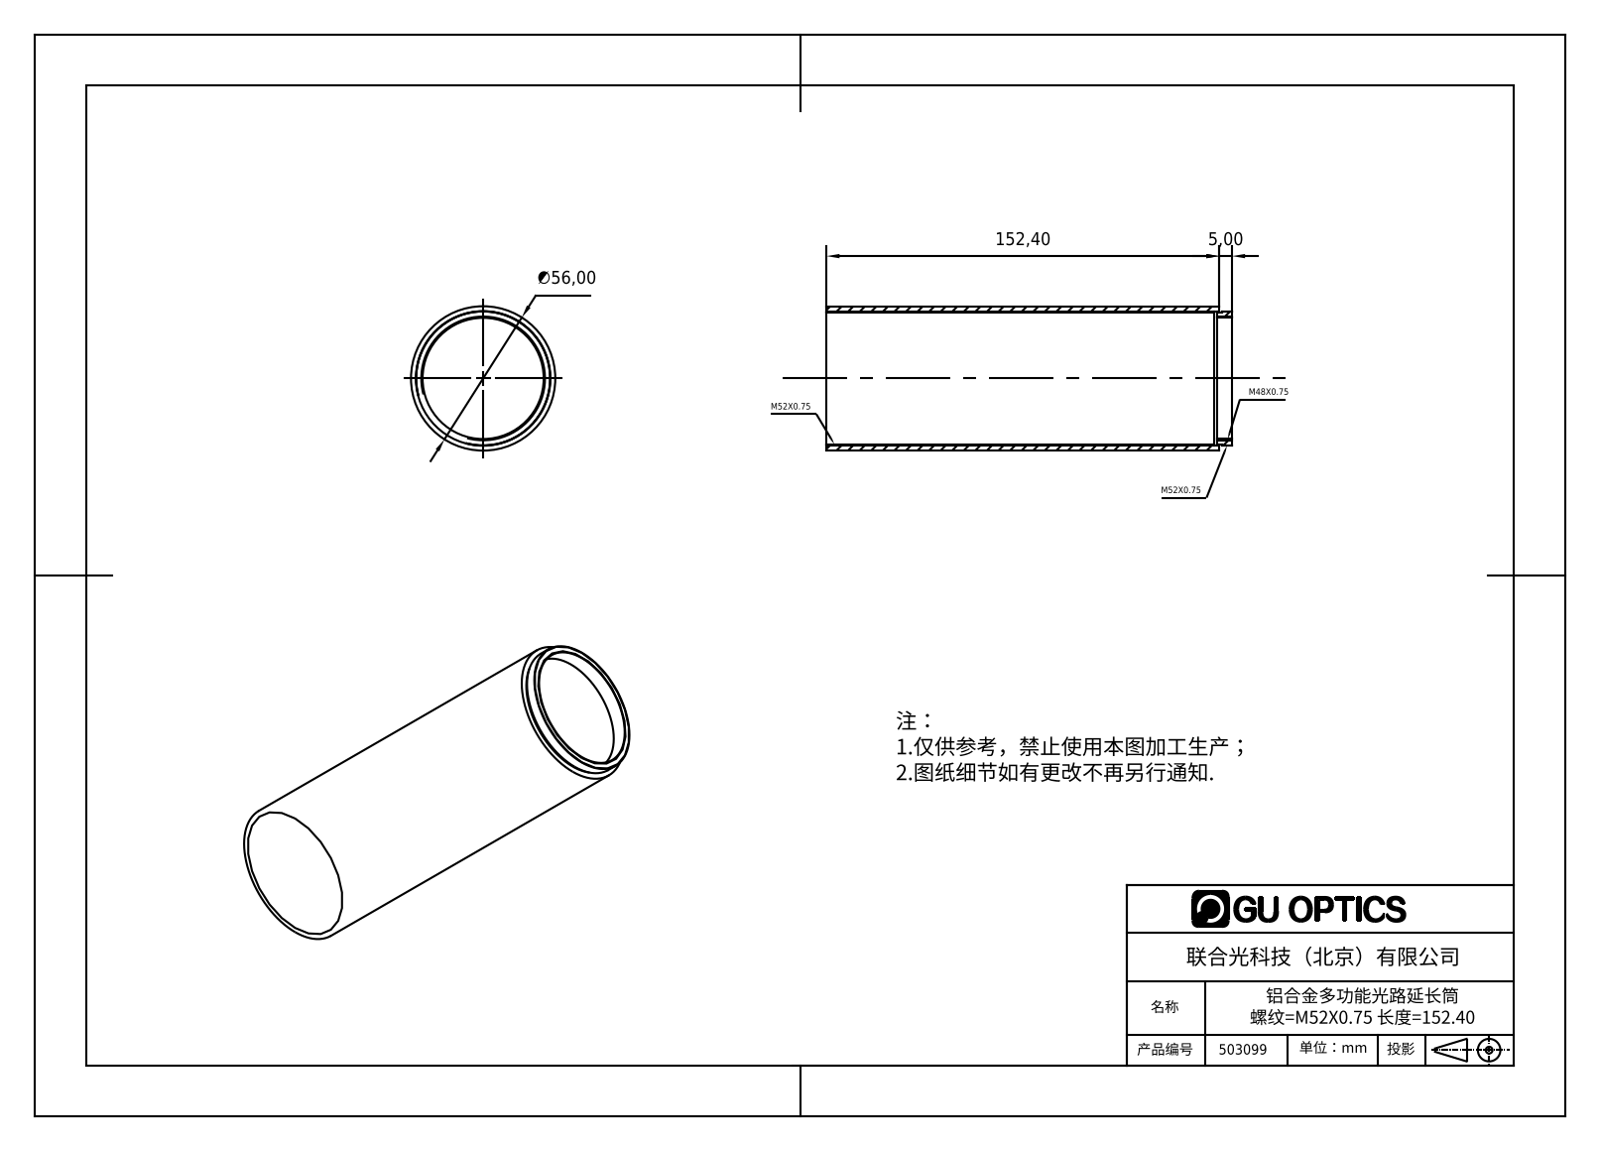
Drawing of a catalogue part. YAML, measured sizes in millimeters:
part_name: "503099"
step_written_by: "SolidWorks 2016 (AUTOMOTIVE_DESIGN)"
units: millimeters
bodies: {solids: 1, faces: 18, planar: 6, cylindrical: 12, other: 0}
overall_size: [157.4, 56, 56]
volume: 66176
surface_area: 54620
round_holes:
  - {diameter: 47, count: 1}
  - {diameter: 51, count: 1}
  - {diameter: 52.2, count: 1}
round_bosses_or_shafts:
  - {diameter: 56, count: 1}
face_to_face_distances: [1, 152.4, 157.4, 5, 151.4, 6, 2, 153.4, 4, 150.4]
